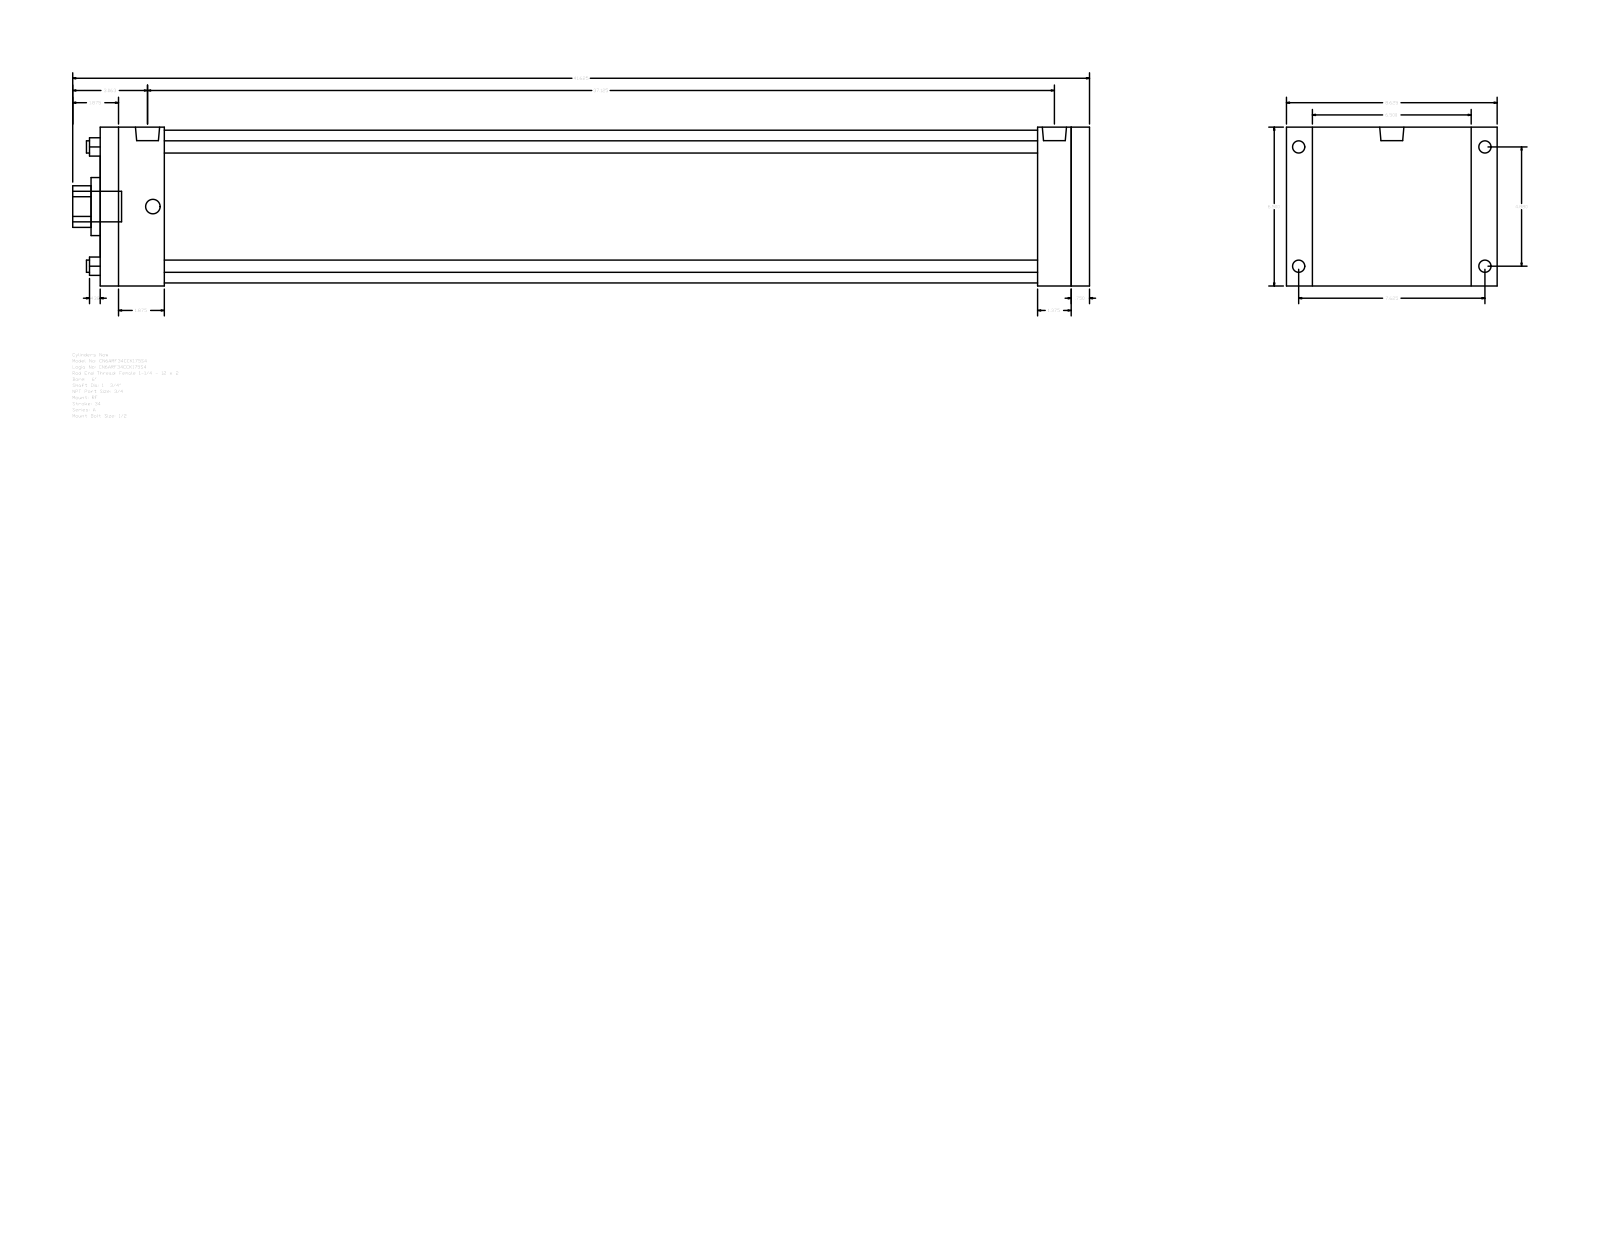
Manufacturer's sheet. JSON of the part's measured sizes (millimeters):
{"part_name": "A_RF__0600_1.75", "step_written_by": "GSSL Pune (CONFIG_CONTROL_DESIGN)", "units": "millimeters", "bodies": {"solids": 0, "faces": 92, "planar": 64, "cylindrical": 28, "other": 0}, "overall_size": [1057.28, 219.07, 165.1], "round_holes": [[12.7, 4], [44.45, 1], [60.33, 1], [158.75, 1]], "round_bosses_or_shafts": [[15.08, 4], [12.7, 4], [25.12, 2], [31.75, 1]], "partial_cylinders_radius": [[21.63, 1]], "face_to_face_distances": [165.1, 1028.71, 1009.65, 19.06, 34.92, 66.68, 942.97, 962.03, 974.73, 908.05], "hole_center_spacings": [87.65, 123.96, 175.31]}
